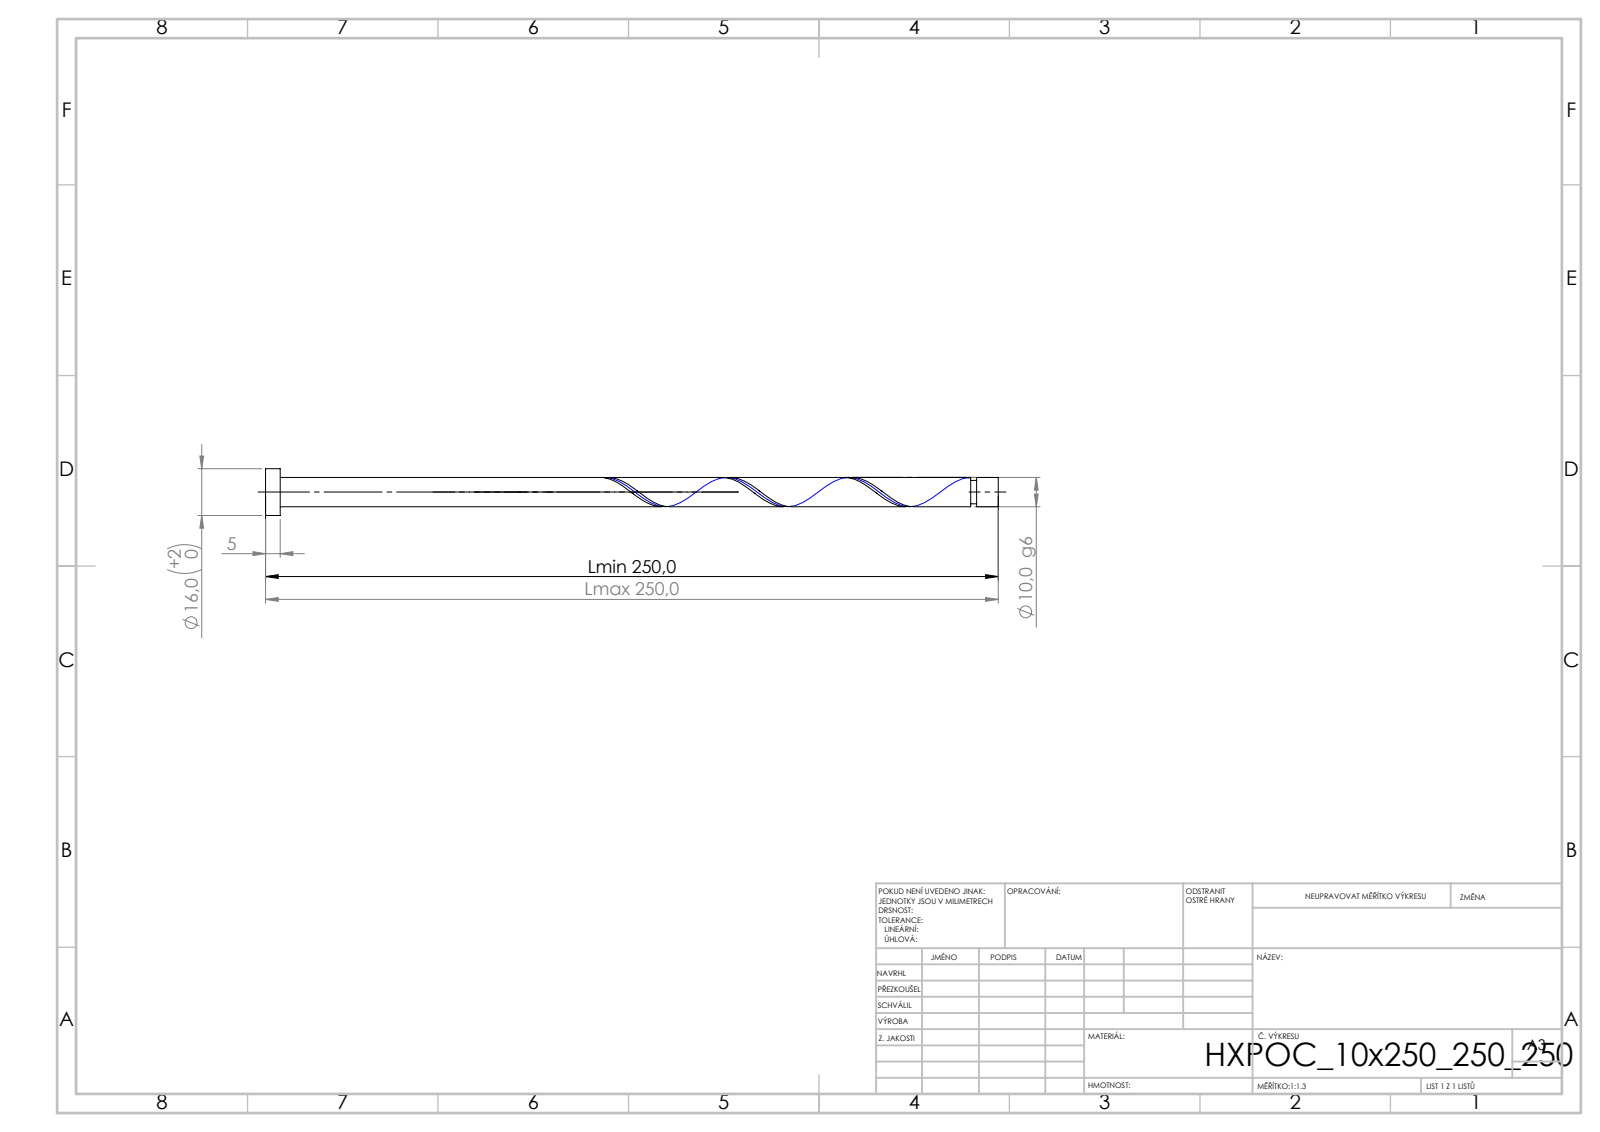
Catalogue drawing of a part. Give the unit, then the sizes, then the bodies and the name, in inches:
Units: inches
Overall size (bounding box): 9.843 × 0.63 × 0.63
Round bosses / shafts (diameter × count): ⌀0.63 ×1, ⌀0.394 ×1, ⌀0.315 ×1
Main face-to-face distances: 0.197, 9.843, 9.646, 9.552, 9.355, 0.291, 9.473, 9.276, 0.079, 0.37
Volume: 1.221 in³ · Surface area: 13.26 in²
Bodies: 1 solid, 21 faces (6 planar, 14 cylindrical, 1 other)
STEP written by: SolidWorks 2019 (CONFIG_CONTROL_DESIGN)
